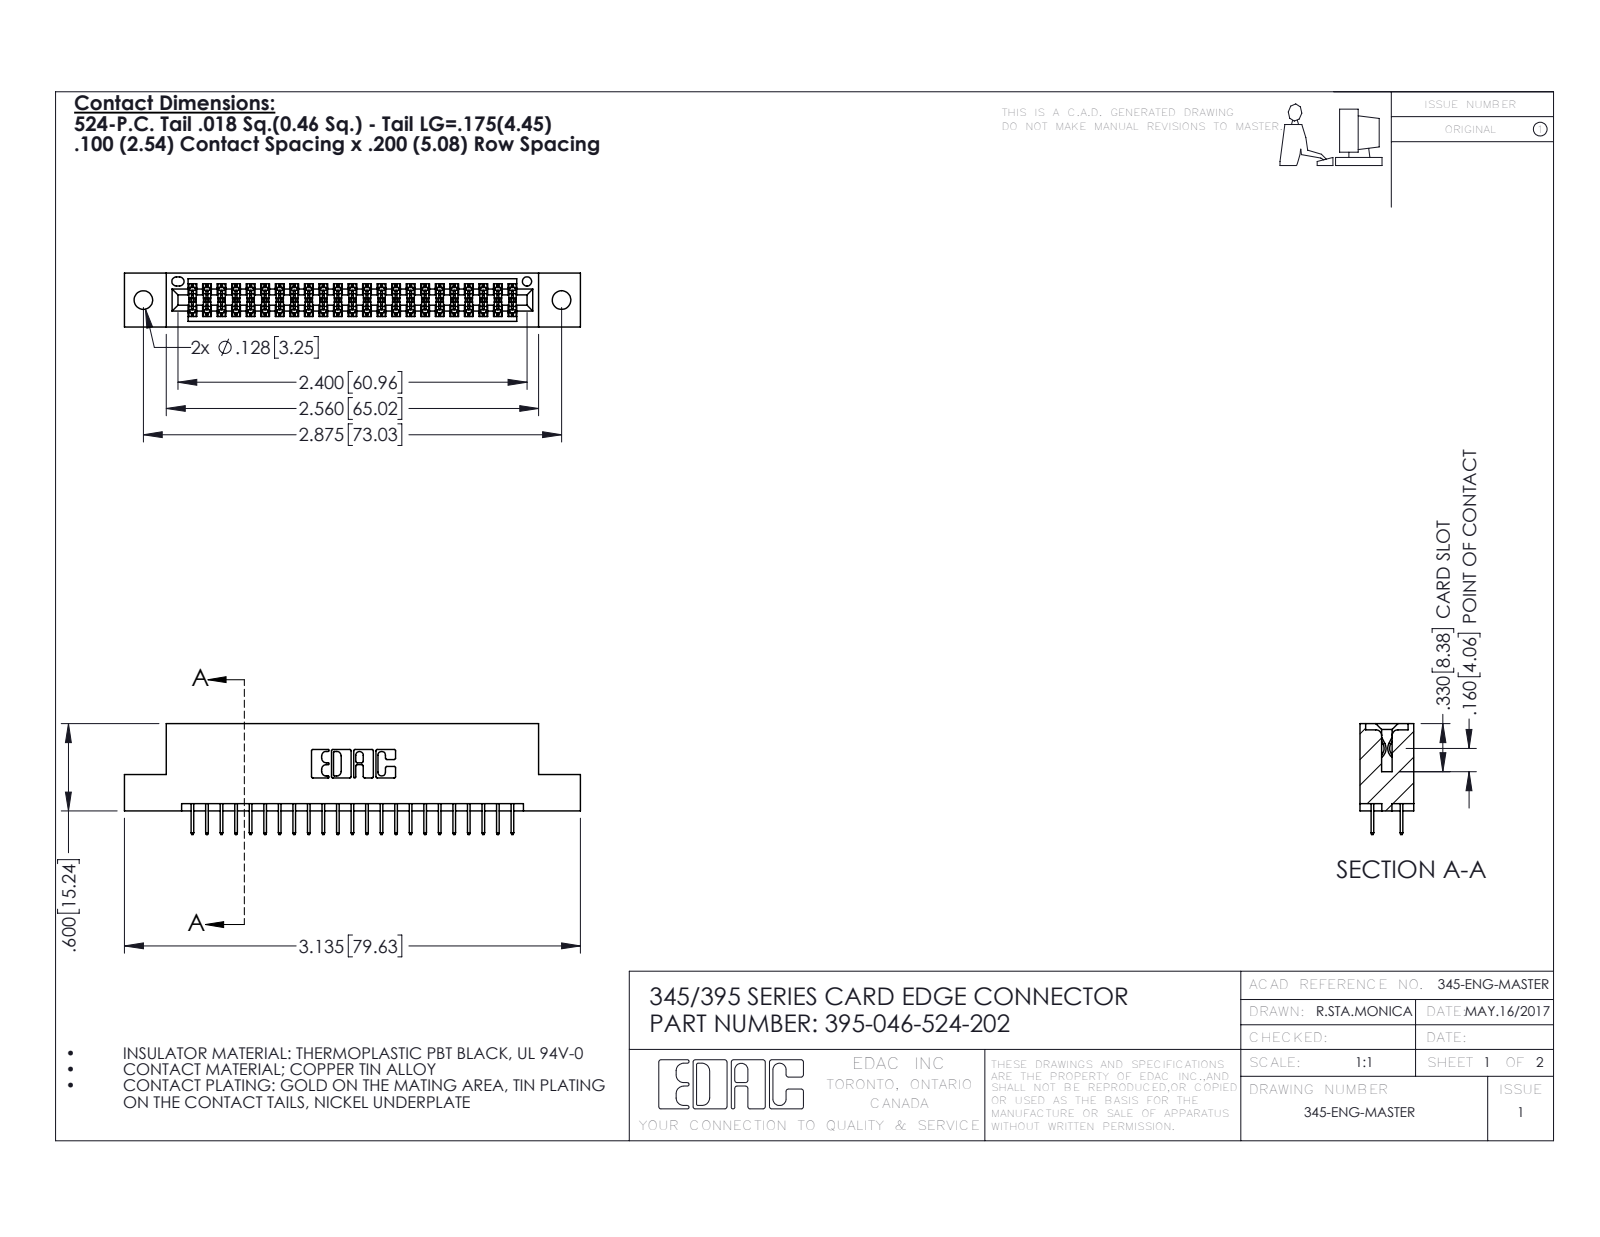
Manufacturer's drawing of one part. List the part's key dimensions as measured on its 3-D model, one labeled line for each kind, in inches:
Part name (STEP PRODUCT): 395-046-524-202; 345 Part_Flush Mounting Lugs - 0.128 Dia; 345-292-001_345-293-124
STEP written by: SolidWorks 2016 (CONFIG_CONTROL_DESIGN)
Units: inches
Bodies: 47 solids, 2610 faces (1874 planar, 736 cylindrical, 0 other)
Overall size (bounding box): 3.135 × 0.762 × 0.37
Volume: 0.455 in³ · Surface area: 15.8 in²
Round holes (diameter × count): ⌀0.128 ×2, ⌀0.064 ×1
Partial cylindrical surfaces — rounded edges, fillets, slot ends (radius × count): R0.006 ×69, R0.01 ×22, R0.007 ×6, R0.031 ×6, R0.026 ×3, R0.014 ×2, R0.019 ×2, R0.022 ×2
Main face-to-face distances: 0.298, 0.072, 0.2, 0.37, 0.098, 0.272, 0.025, 0.225, 0.072, 0.175
Hole centre spacings: 0.27, 2.641, 2.875
